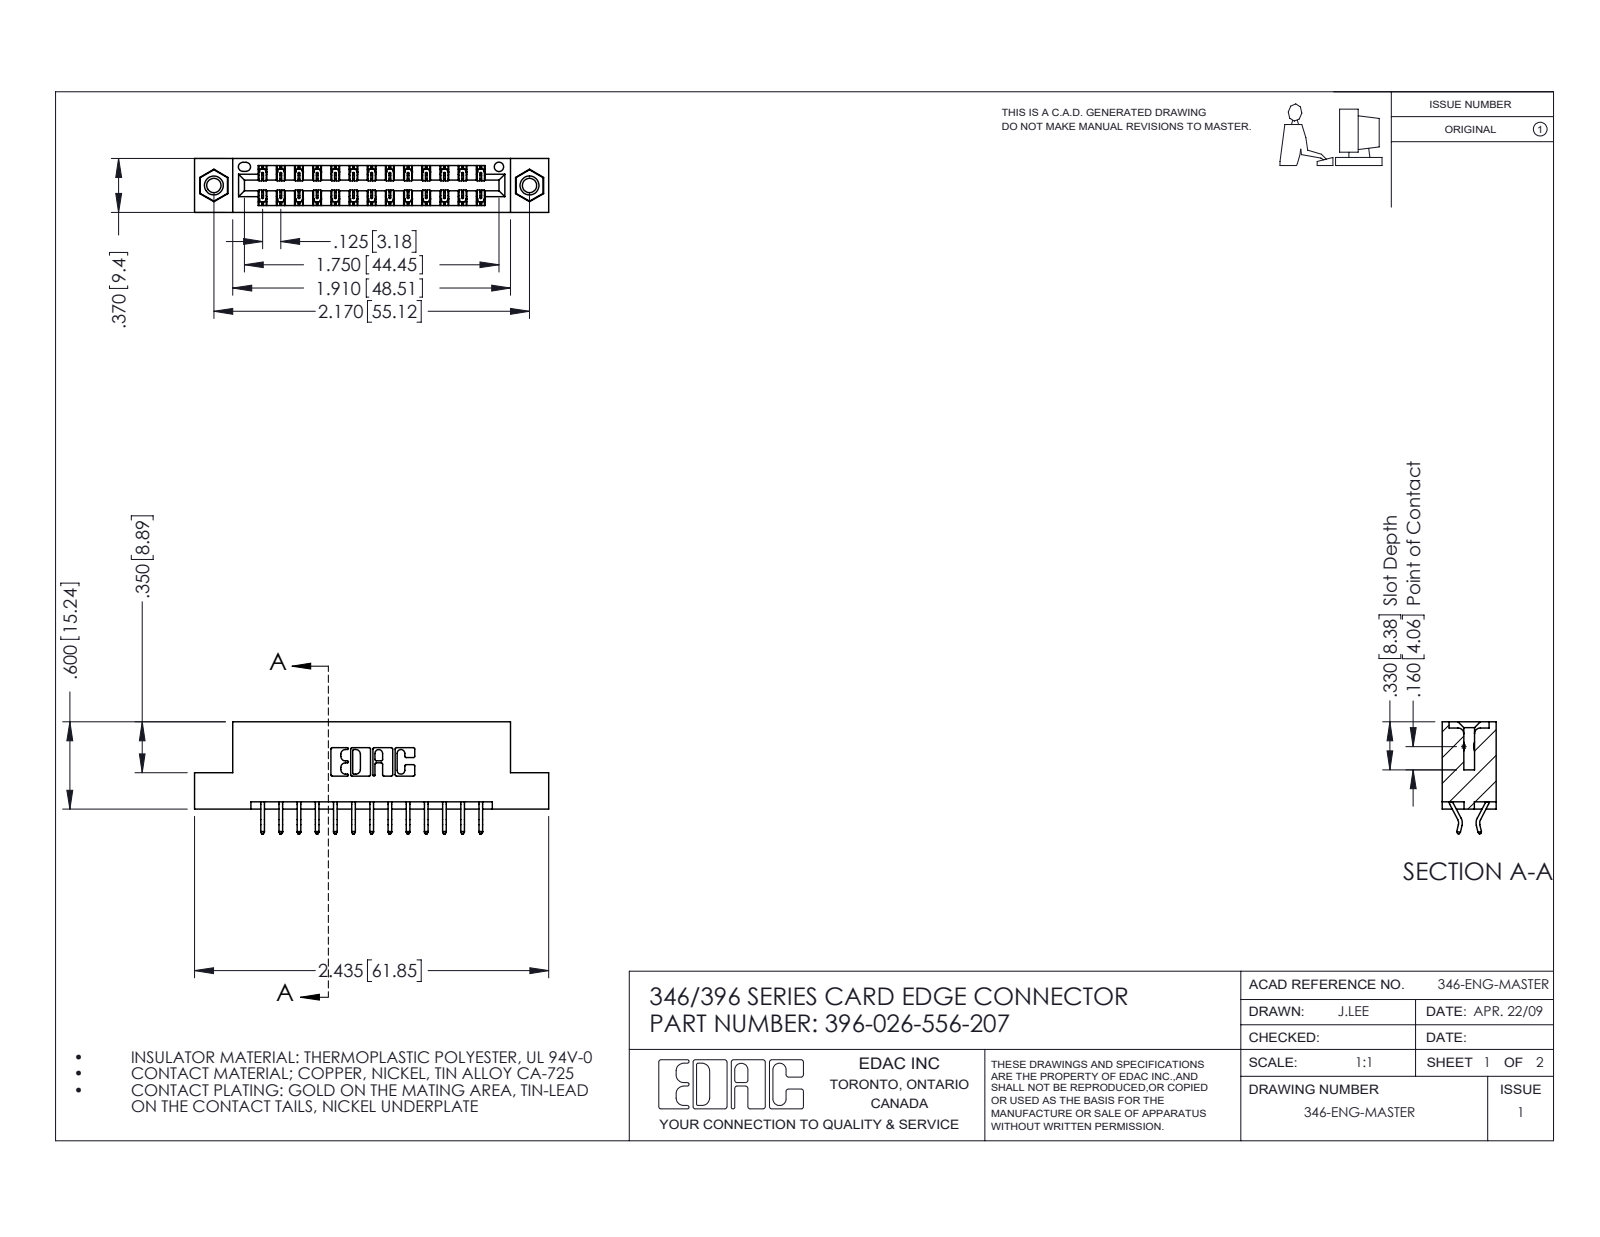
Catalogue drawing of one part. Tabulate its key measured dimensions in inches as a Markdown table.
| quantity | value |
| --- | --- |
| part name | 346 Part_Flush Mounting Lugs - 0.156 Dia-TI; 345-250-001_345-250-005-103; 396-026-556-207; 345-292-001_556 Tail |
| STEP written by | SolidWorks 2016 (CONFIG_CONTROL_DESIGN) |
| units | inches |
| bodies | 29 solids, 1690 faces (1122 planar, 552 cylindrical, 16 other) |
| overall size | 2.435 × 0.77 × 0.37 |
| volume | 0.353 in³ |
| surface area | 11.65 in² |
| round holes (diameter × count) | 0.098 × 2, 0.125 × 2, 0.156 × 2, 0.064 × 1 |
| round bosses / shafts (diameter × count) | 0.155 × 2 |
| partial cylindrical surfaces (radius × count) | 0.006 × 39, 0.01 × 22, 0.007 × 6, 0.031 × 6, 0.026 × 3, 0.01 × 2, 0.014 × 2, 0.022 × 2 |
| main face-to-face distances | 0.25, 0.048, 0.322, 0.37, 0.025, 0.072, 0.298, 0.275, 0.148, 0.222 |
| hole center spacings | 0.246, 1.964, 2.17 |
